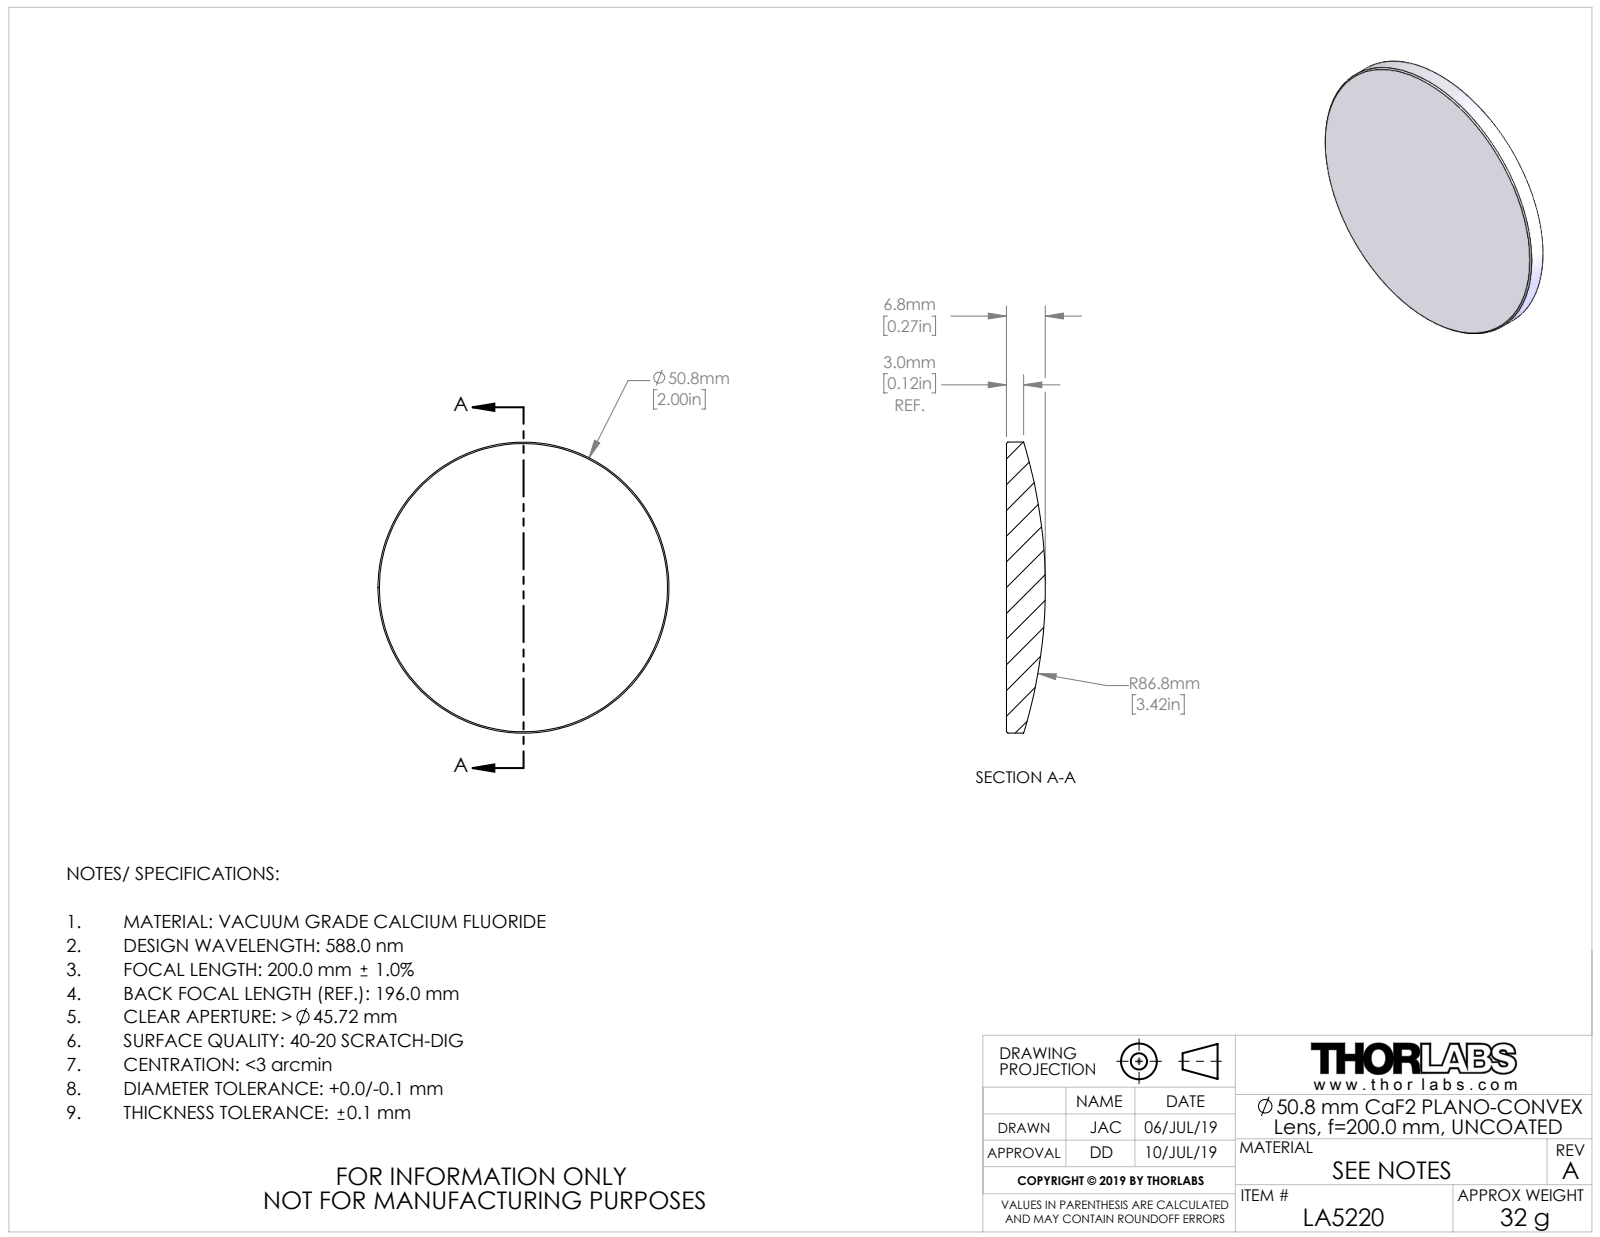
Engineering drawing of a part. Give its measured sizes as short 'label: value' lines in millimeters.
name: TTN188098-E0W
written by: SolidWorks 2018 (CONFIG_CONTROL_DESIGN)
unit: mm
bodies: 1 solid, 7 faces (1 planar, 2 cylindrical, 4 other)
size: 50.8 × 50.8 × 6.8
volume: 9 954 mm³; area: 4 554 mm²
bosses: 1× ⌀50.8
